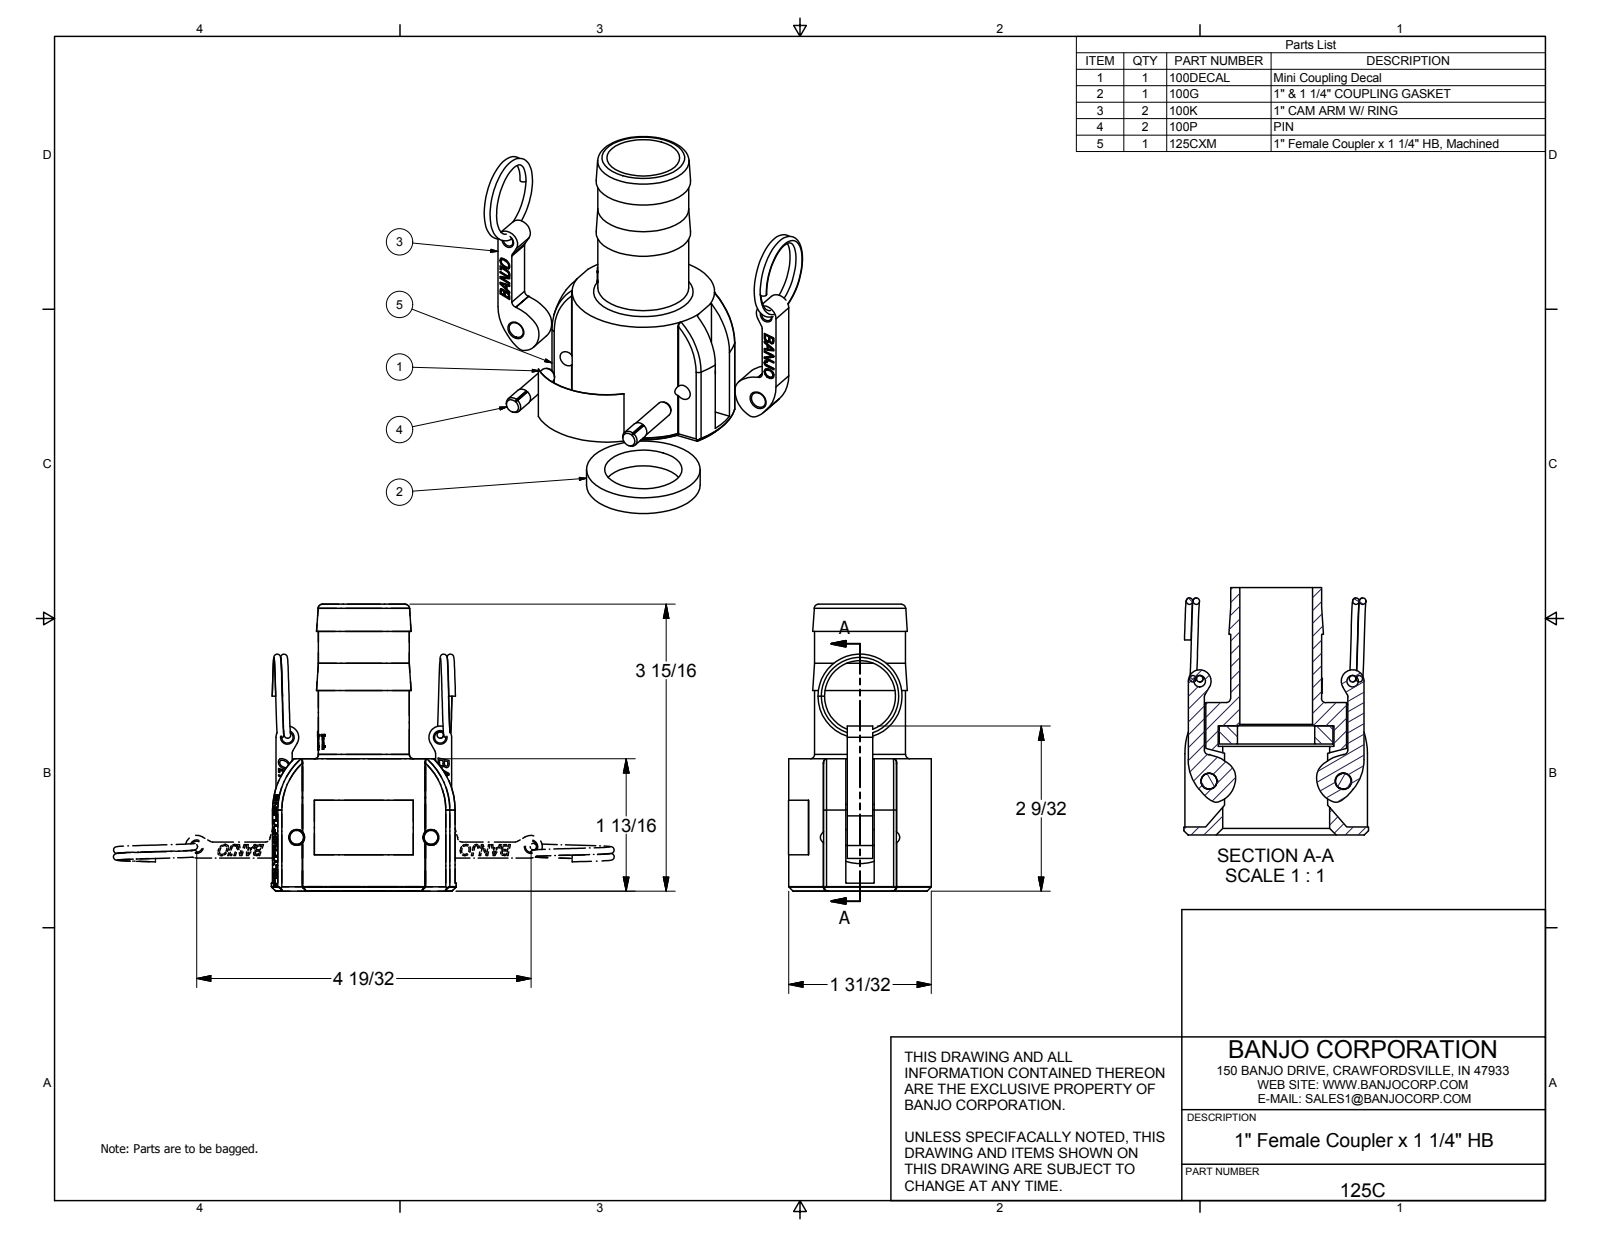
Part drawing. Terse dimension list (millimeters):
name: 125CX; 125CXM; 100G; 100P (+6 more)
written by: Autodesk Inventor 2014 (AUTOMOTIVE_DESIGN)
unit: mm
bodies: 9 solids, 833 faces (412 planar, 90 cylindrical, 331 other)
size: 100.2 × 64.52 × 49.85
volume: 77 437 mm³; area: 39 924 mm²
holes: 2× ⌀3.96, 2× ⌀5.56, 2× ⌀5.71, 1× ⌀25.4, 1× ⌀26.99, 1× ⌀37.34, 1× ⌀40.49
bosses: 2× ⌀5.77, 2× ⌀5.51, 1× ⌀39.69, 1× ⌀31.75
rounds: 6× R1.52, 4× R0.25, 2× R1.59, 2× R1.59, 2× R3.97, 2× R15.88, 1× R16.13, 1× R24.89
face distances: 0.51, 9.4, 8.12, 9.91, 8.89, 6.35, 14.47, 31.75, 38.1, 46.22
hole spacings: 35.08, 61.12, 46.92, 53.4
